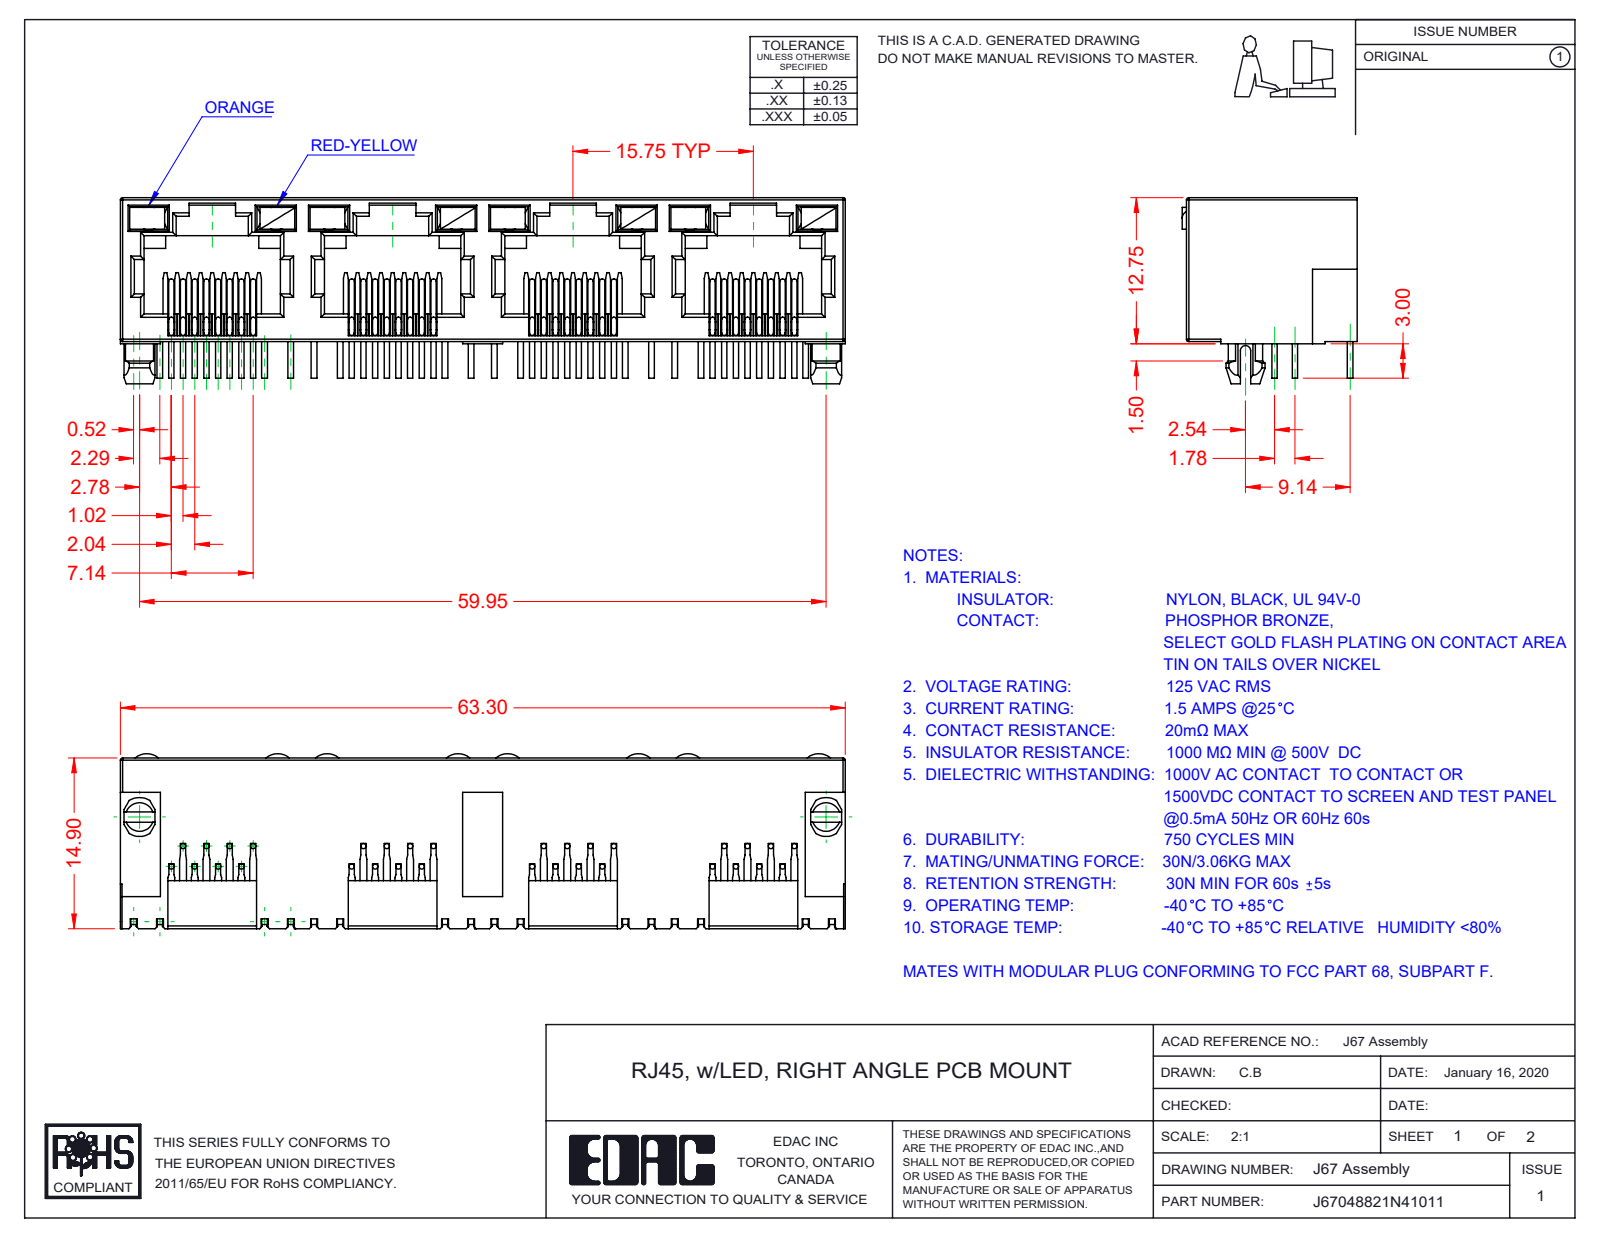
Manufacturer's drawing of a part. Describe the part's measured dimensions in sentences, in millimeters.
The part is named "67 Contacts; 67 LED LH_4-Orange; J67048822N48011; 67 Insulator (+1 more)". Its 3-D file was written by "SolidWorks 2016 (CONFIG_CONTROL_DESIGN)". It is 41 solids with 2473 faces: 1781 planar, 484 cylindrical and 208 other. Overall it measures 63.3 by 16.25 by 15.28 millimeters. Its volume is 5 159 cubic millimeters and its surface area 11 573 square millimeters. Round bosses or shafts: 96 of diameter 0.46. Partial cylindrical surfaces (rounded edges, fillets, slot ends): 66 of radius 0.2, 29 of radius 0.3, 9 of radius 0.45, 8 of radius 1.55, 2 of radius 1.5, 2 of radius 1.7, 1 of radius 0.35, 1 of radius 1. The main face-to-face distances are 0.5, 12.55, 1.89, 0.89, 10, 15.75, 1, 1.39, 11, 11.89.
